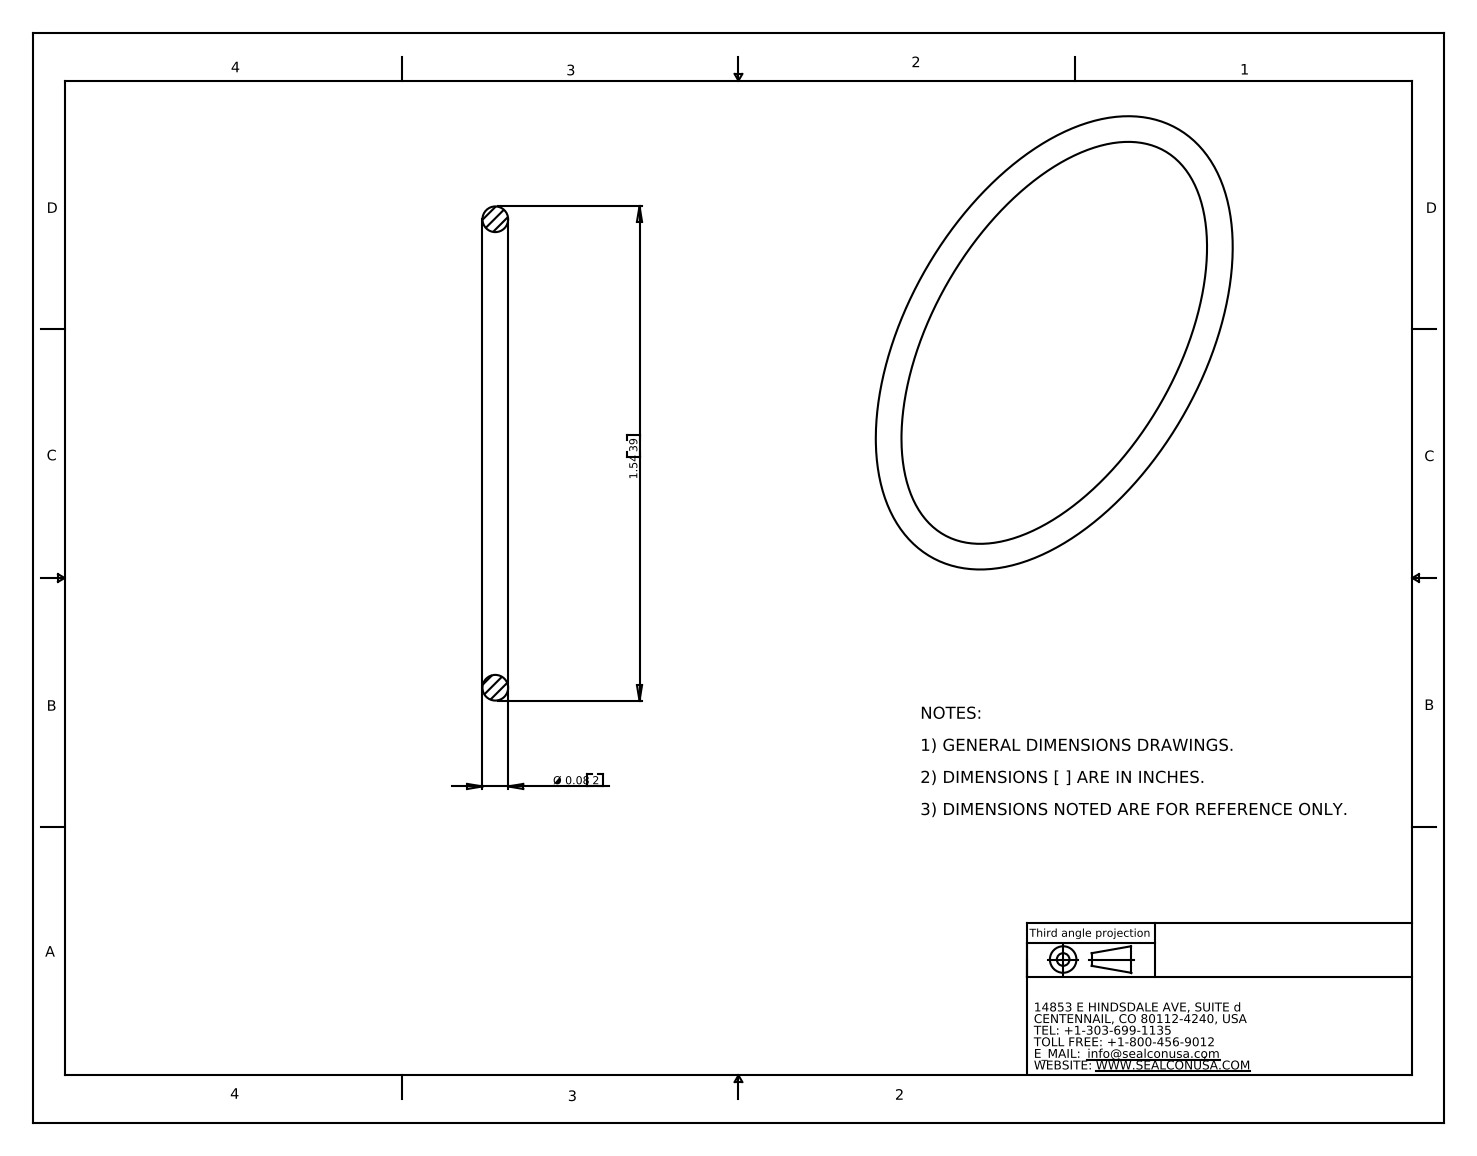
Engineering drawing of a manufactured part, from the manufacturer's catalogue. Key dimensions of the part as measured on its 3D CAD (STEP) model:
Part name (STEP PRODUCT): OM-40-VT
STEP written by: SolidWorks 2007 (CONFIG_CONTROL_DESIGN)
Units: inches
Bodies: 1 solid, 4 faces (0 planar, 0 cylindrical, 4 other)
Overall size (bounding box): 1.54 × 1.54 × 0.08
Volume: 0.023 in³ · Surface area: 1.153 in²
